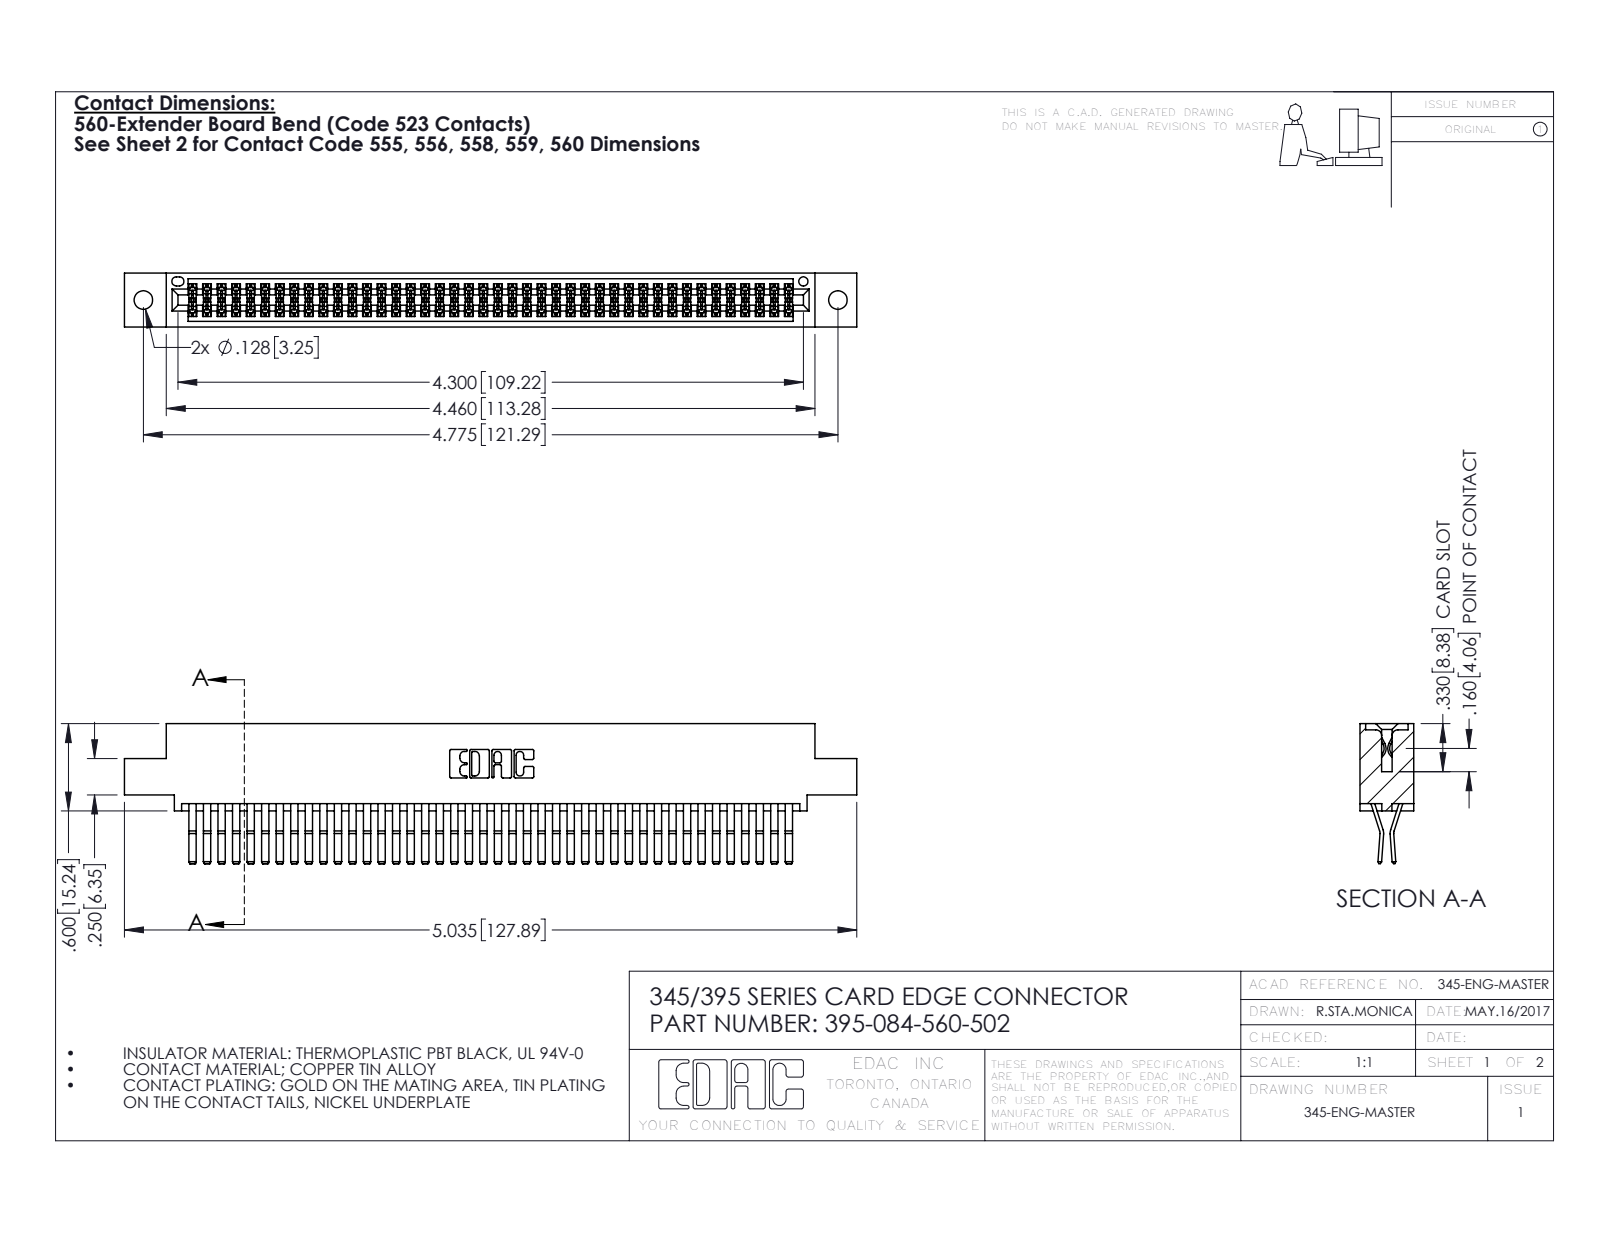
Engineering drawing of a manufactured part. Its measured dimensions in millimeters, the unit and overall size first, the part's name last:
Units: millimetres
Overall size (bounding box): 127.9 × 24.4 × 9.4
Round holes (diameter × count): ⌀3.3 ×2, ⌀1.6 ×1
Partial cylindrical surfaces — rounded edges, fillets, slot ends (radius × count): R0.2 ×126, R0.3 ×22, R0.2 ×6, R0.8 ×6, R0.7 ×3, R0.3 ×2, R0.4 ×2, R0.5 ×2
Main face-to-face distances: 0.6, 7.6, 1.8, 9.4, 5.1, 2.5, 6.9, 5.7, 4.4, 3.8
Hole centre spacings: 6.9, 115.3, 121.3
Volume: 12 900 mm³ · Surface area: 20 250 mm²
Bodies: 85 solids, 4498 faces (2856 planar, 1642 cylindrical, 0 other)
Part name (STEP PRODUCT): 395-084-560-502; 345 Part_0.110 Offset - 0.128 Dia; 345-292-001_560 Tail
STEP written by: SolidWorks 2016 (CONFIG_CONTROL_DESIGN)
